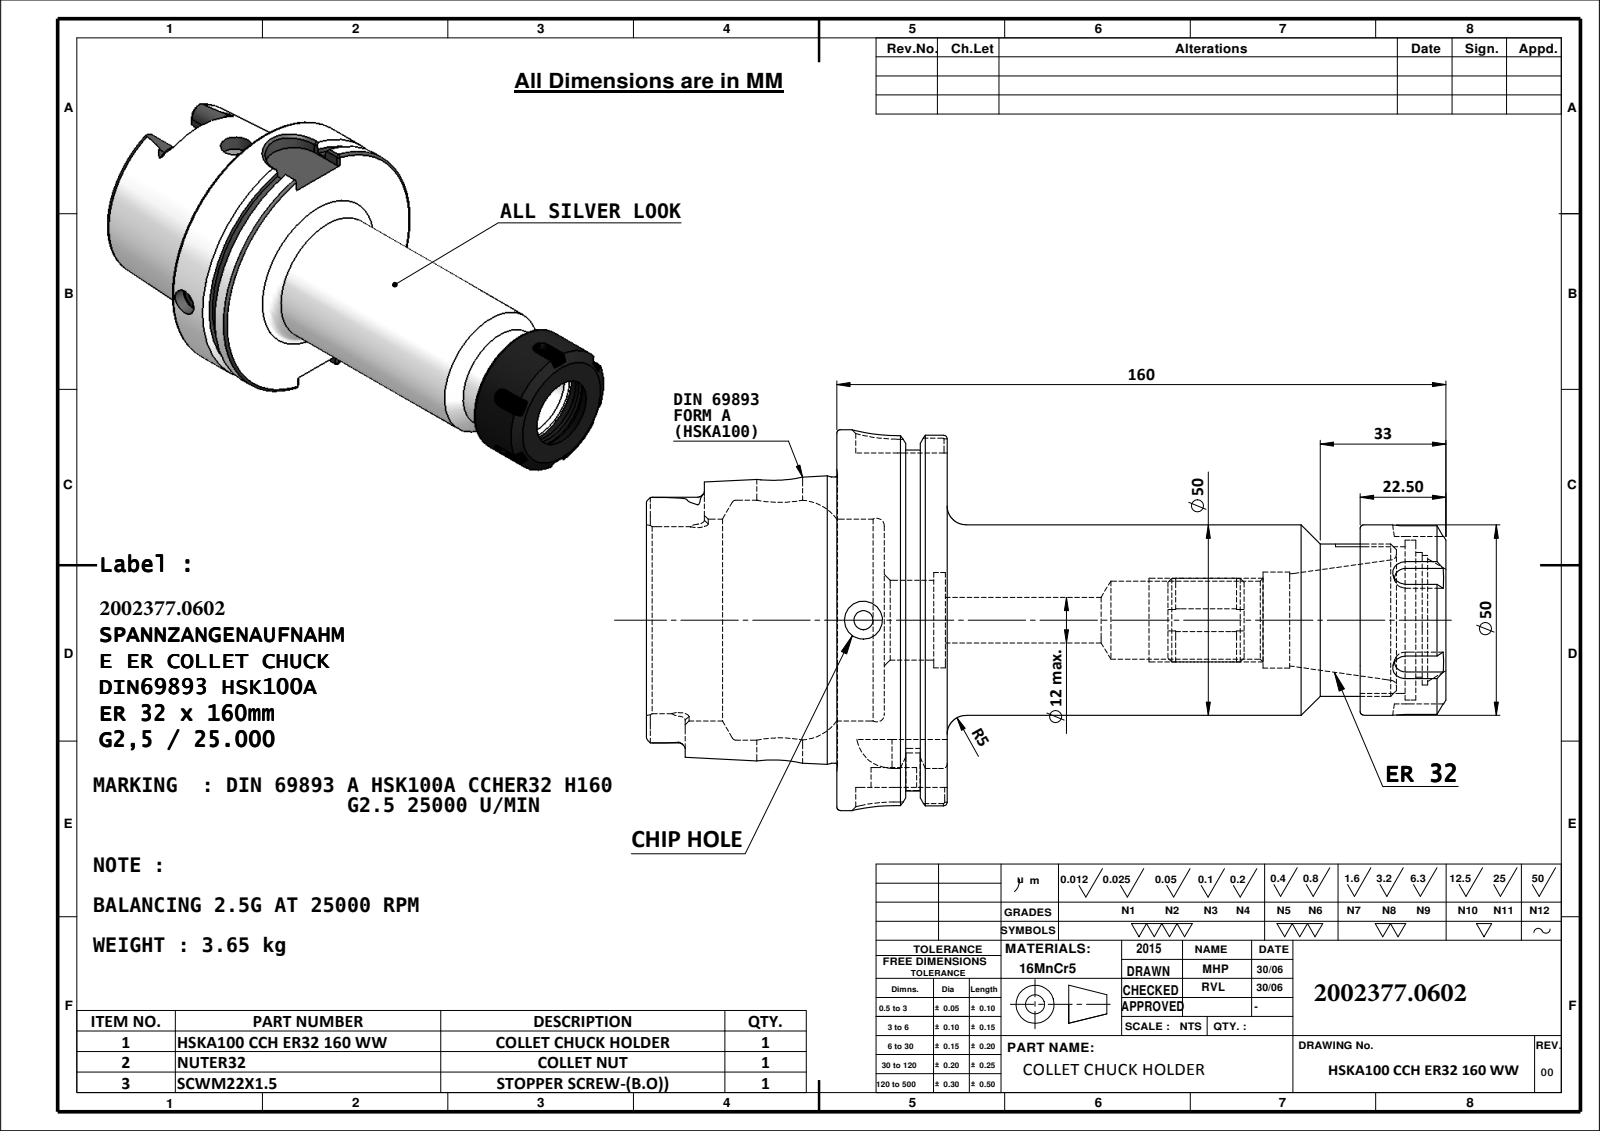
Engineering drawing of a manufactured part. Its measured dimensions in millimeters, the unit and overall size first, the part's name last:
Units: millimetres
Overall size (bounding box): 210 × 100 × 100
Round holes (diameter × count): ⌀12 ×3, ⌀6 ×1, ⌀10 ×1, ⌀20.5 ×1, ⌀21 ×1, ⌀25 ×1, ⌀25.2 ×1, ⌀32.8 ×1, ⌀34 ×1, ⌀38.5 ×1, ⌀42 ×1, ⌀53 ×1
Round bosses / shafts (diameter × count): ⌀100 ×1, ⌀92 ×1, ⌀75.16 ×1, ⌀50 ×1, ⌀40 ×1, ⌀22 ×1
Partial cylindrical surfaces — rounded edges, fillets, slot ends (radius × count): R1.8 ×6, R4.88 ×4, R10 ×2, R11 ×1
Main face-to-face distances: 29, 12.5, 16.5, 50, 62.5, 79, 210, 160, 147.5, 131
Hole centre spacings: 1.6, 30
Volume: 456 474 mm³ · Surface area: 85 368 mm²
Bodies: 3 solids, 261 faces (95 planar, 68 cylindrical, 98 other)
Part name (STEP PRODUCT): 91100A-ER8 32160; HSKA100 CCH ER32 160 WW; FTNUTER32; FTSCWM22X1.5
STEP written by: SolidWorks 2009 (CONFIG_CONTROL_DESIGN)
